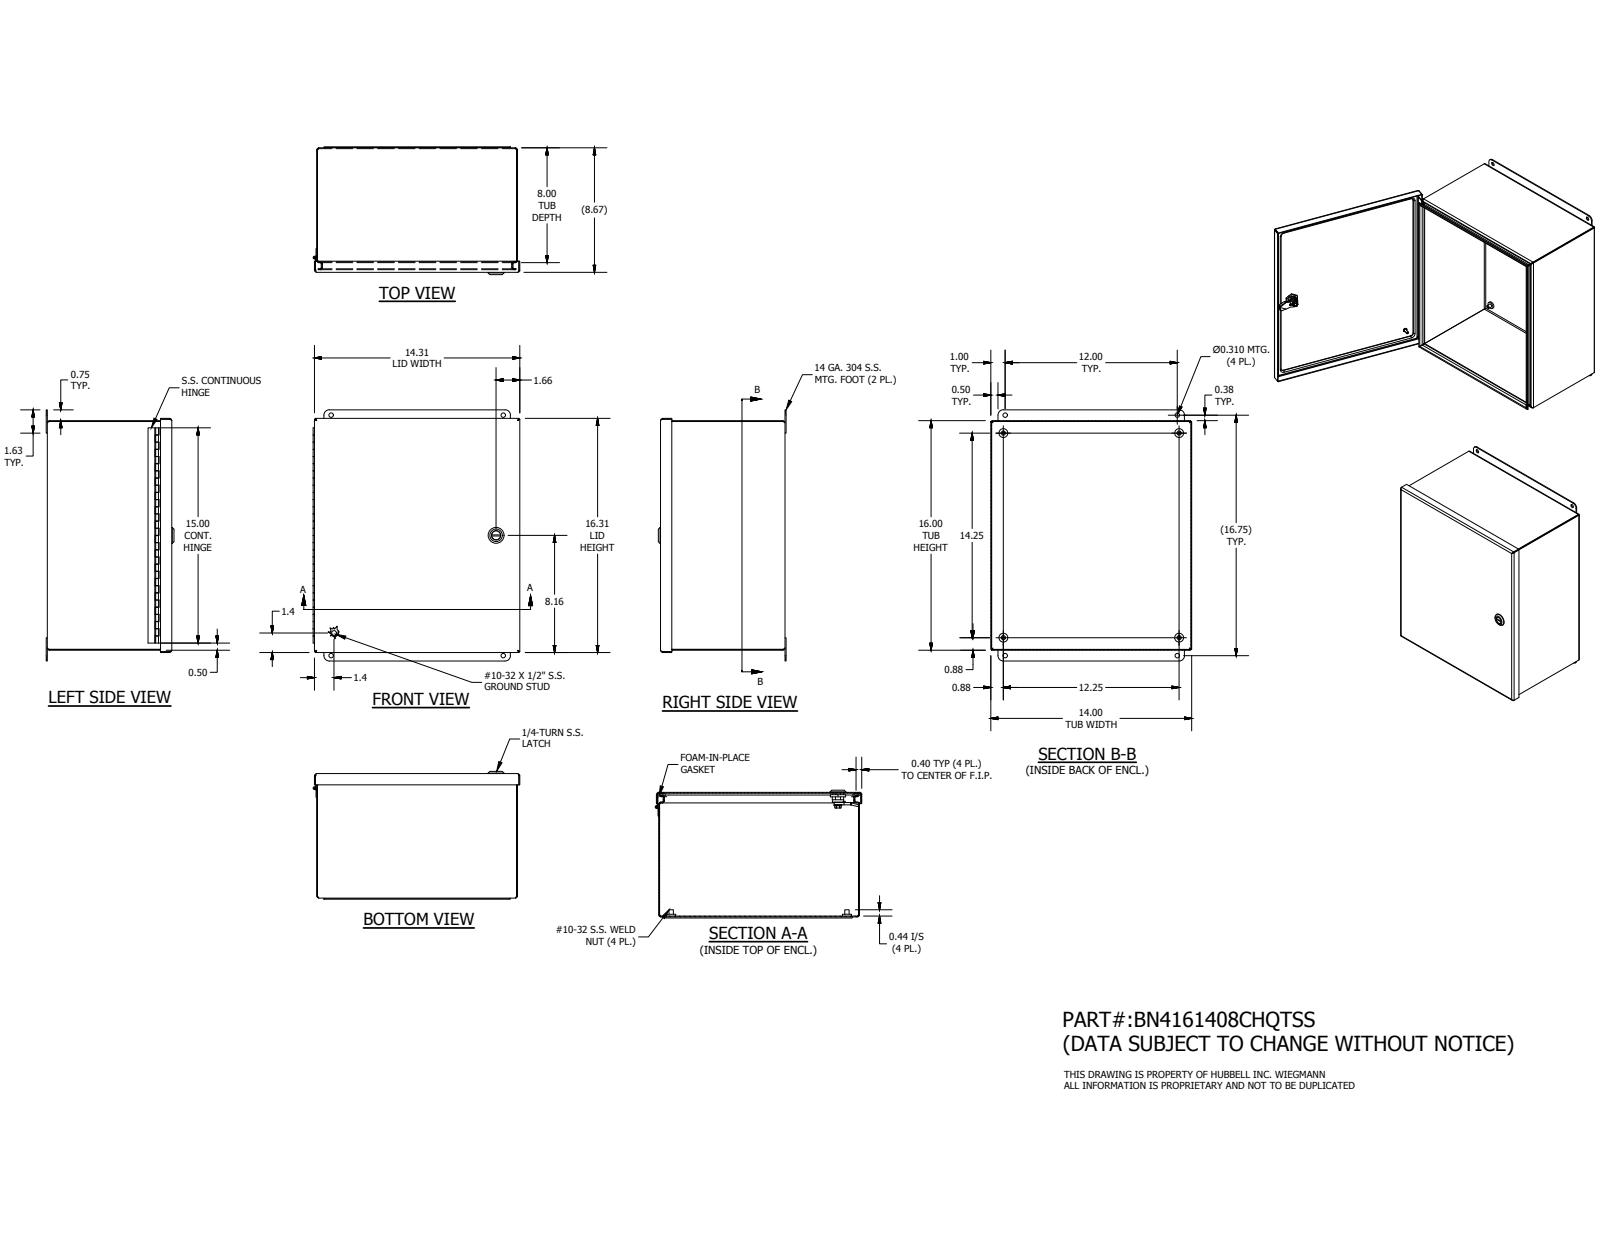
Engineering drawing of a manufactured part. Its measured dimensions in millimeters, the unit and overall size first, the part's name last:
Units: millimetres
Overall size (bounding box): 444.5 × 366.06 × 226.19
Round holes (diameter × count): ⌀3.96 ×4, ⌀7.87 ×4, ⌀2.96 ×1, ⌀5 ×1, ⌀8 ×1, ⌀10 ×1, ⌀10.2 ×1, ⌀16.1 ×1
Round bosses / shafts (diameter × count): ⌀15.88 ×4, ⌀7.62 ×4, ⌀28 ×1, ⌀19.8 ×1, ⌀16 ×1, ⌀15.2 ×1, ⌀13.5 ×1, ⌀12.8 ×1
Partial cylindrical surfaces — rounded edges, fillets, slot ends (radius × count): R2.38 ×20, R3.88 ×20, R3.17 ×16, R0.5 ×8, R4 ×4, R9.53 ×4, R2.31 ×2, R6.45 ×1
Main face-to-face distances: 1.5, 1.49, 218.79, 220.28, 217.29, 218.78, 404.9, 354.11, 355.6, 352.61
Hole centre spacings: 31.91, 393.71, 499.85, 304.8, 309.6, 309.61, 311.15, 346.32
Volume: 1 156 000 mm³ · Surface area: 1 470 000 mm²
Bodies: 19 solids, 668 faces (359 planar, 215 cylindrical, 94 other)
Part name (STEP PRODUCT): BN41614CHQTSSLID; 16x14; 34857; H4050555LH (+8 more)
STEP written by: Autodesk Inventor 2016 (AUTOMOTIVE_DESIGN)
